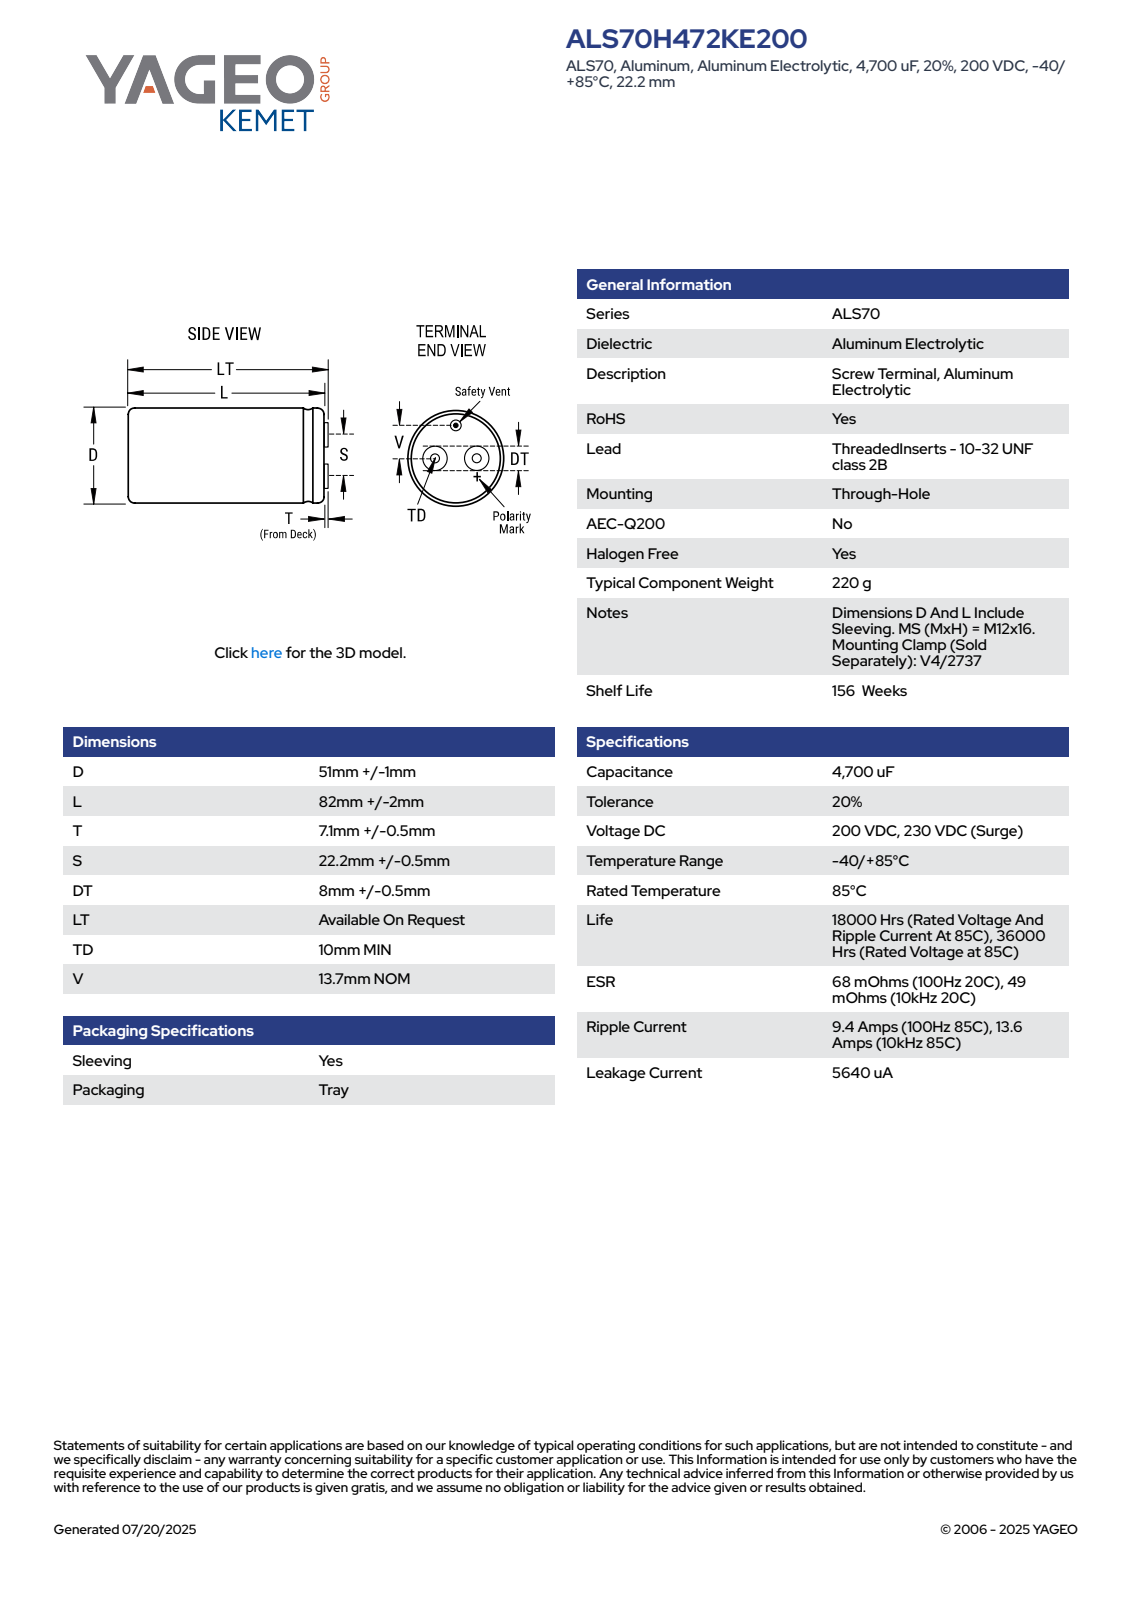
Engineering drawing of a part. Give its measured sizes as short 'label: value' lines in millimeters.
name: CARC_KAR_51X82_D52L84T7.6S22.2DT8.500TD10.000V13.700
written by: SolidWorks 2014 (AUTOMOTIVE_DESIGN)
unit: mm
bodies: 1 solid, 88 faces (30 planar, 19 cylindrical, 39 other)
size: 91.6 × 52.01 × 52
volume: 178 106 mm³; area: 18 452 mm²
holes: 2× ⌀5, 1× ⌀1.33
bosses: 2× ⌀8.5, 1× ⌀52, 1× ⌀2.27
rounds: 1× R26.01
face distances: 84, 91.6, 7.6, 81.6, 2.4, 10, 84.35, 2.75, 0.35, 7.25
hole spacings: 17.63, 22.2
